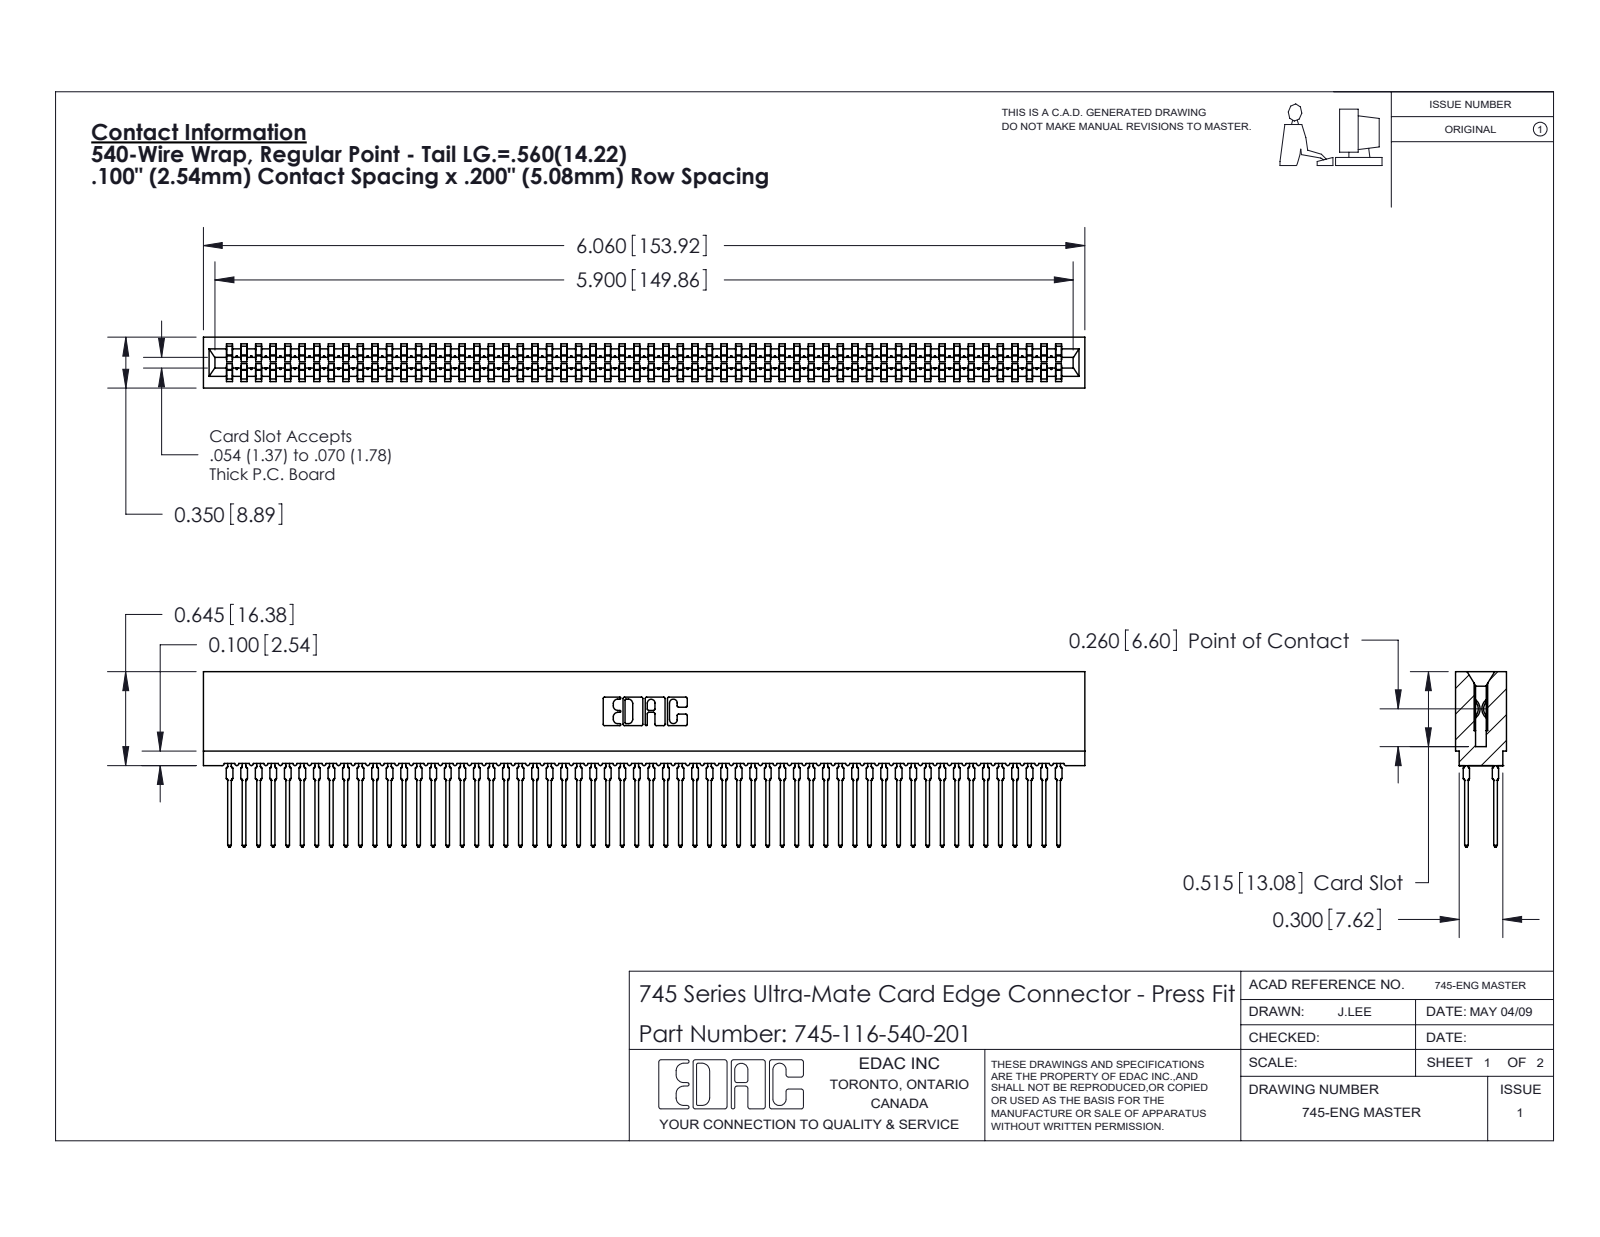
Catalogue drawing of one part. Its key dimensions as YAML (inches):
part_name: "745 Part_Insulator Option - 01; 745-292-001_540; 745-116-540-201"
step_written_by: "SolidWorks 2020 (CONFIG_CONTROL_DESIGN)"
units: inches
bodies: {solids: 117, faces: 10477, planar: 5391, cylindrical: 2070, other: 3016}
overall_size: [6.06, 1.206, 0.35]
volume: 0.861
surface_area: 47.11
partial_cylinders:
  - {radius: 0.021, count: 232}
  - {radius: 0.015, count: 116}
  - {radius: 0.01, count: 22}
  - {radius: 0.005, count: 8}
  - {radius: 0.011, count: 8}
  - {radius: 0.007, count: 6}
  - {radius: 0.031, count: 6}
  - {radius: 0.026, count: 3}
face_to_face_distances: [0.063, 0.287, 0.35, 0.2, 0.045, 0.305, 0.018, 0.243, 0.138, 0.212]
